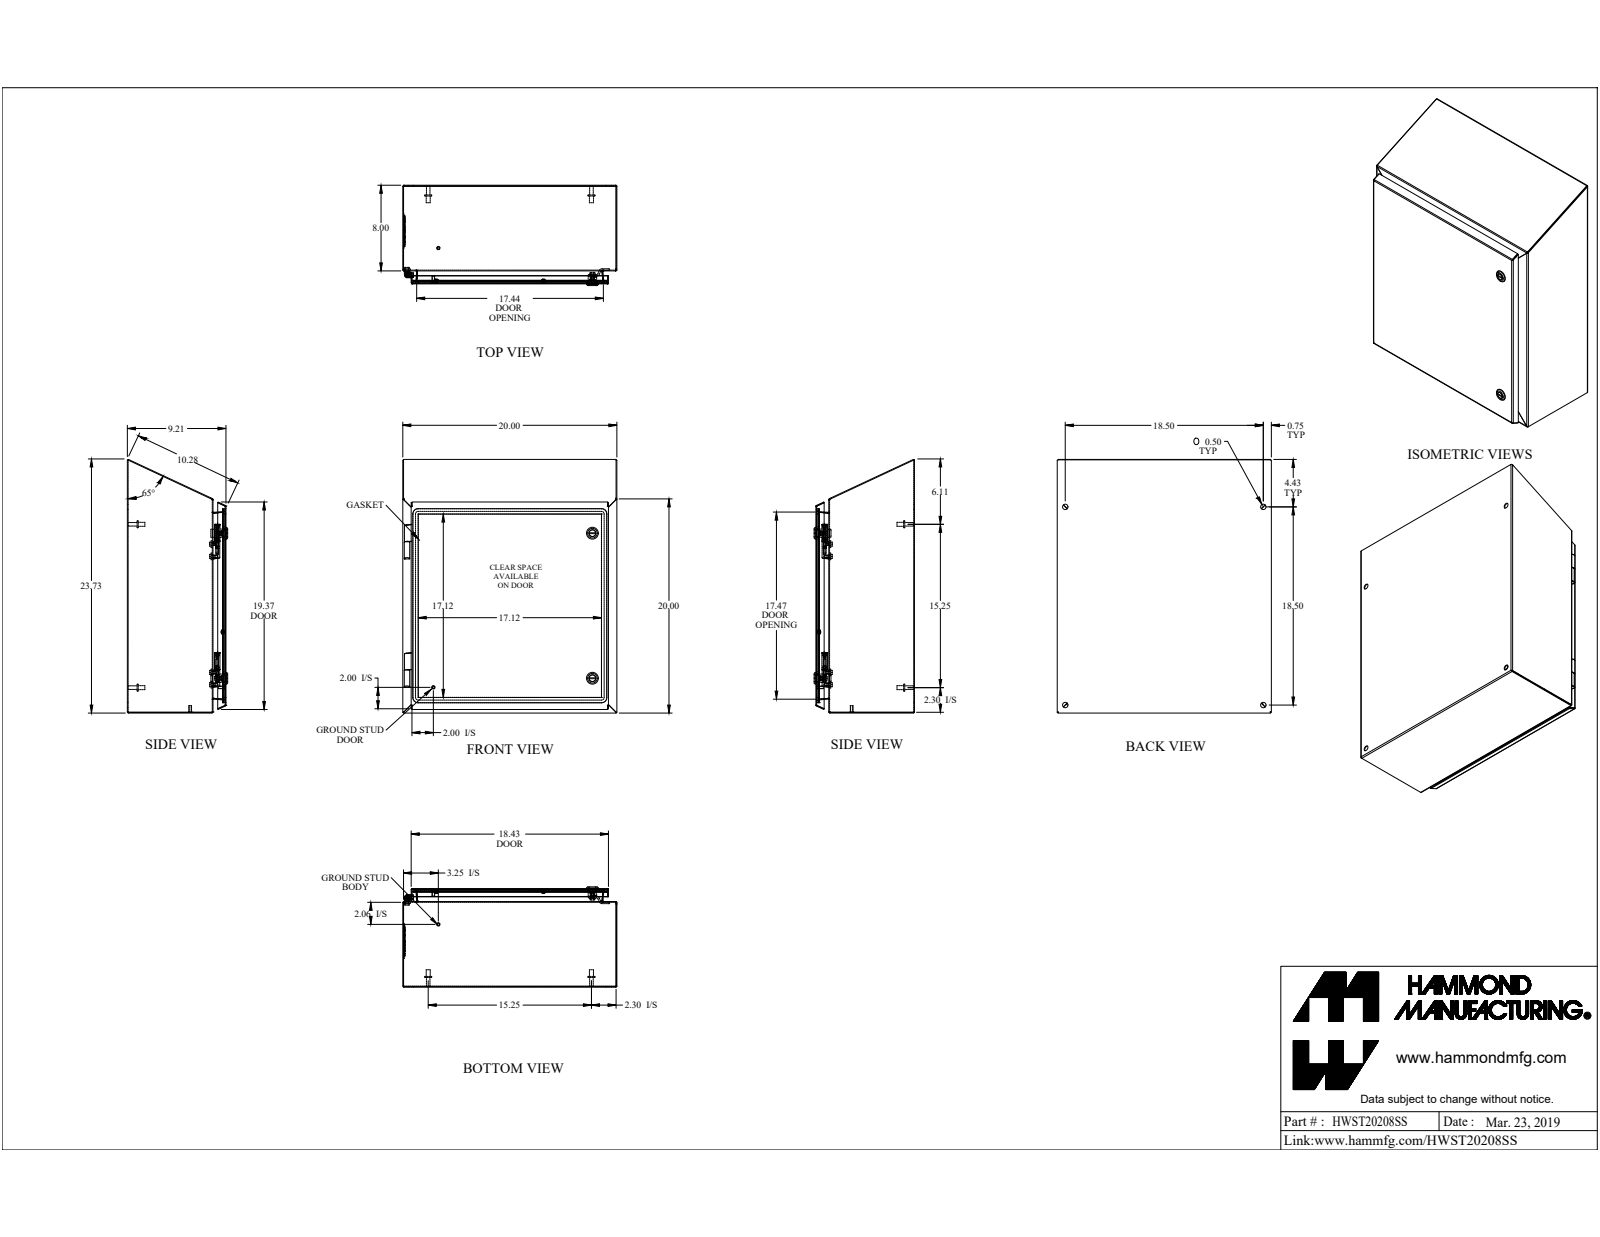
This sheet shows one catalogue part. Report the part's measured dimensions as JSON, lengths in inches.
{"part_name": "HWST20208S16", "step_written_by": "SolidWorks 2019 (AUTOMOTIVE_DESIGN)", "units": "inches", "bodies": {"solids": 43, "faces": 1037, "planar": 631, "cylindrical": 292, "other": 114}, "overall_size": [23.684, 20, 9.37], "volume_in3": 141.4, "surface_area_in2": 3810, "round_holes": [[0.194, 8], [0.5, 6], [0.24, 4], [0.275, 4], [0.13, 2], [0.197, 2], [0.387, 2], [0.63, 2], [0.768, 2], [0.24, 1], [3.5, 1]], "round_bosses_or_shafts": [[0.226, 8], [0.625, 6], [0.65, 4], [0.375, 4], [0.332, 4], [0.25, 4], [0.236, 3], [1.1, 2]], "partial_cylinders_radius": [[0.25, 24], [0.039, 16], [0.108, 16], [0.012, 12], [0.036, 12], [0.125, 12], [0.108, 9], [0.036, 7]], "face_to_face_distances": [0.072, 9.066, 9.138, 0.072, 19.928, 9.138, 9.21, 7.928, 19.856, 20], "hole_center_spacings": [1.142, 11.979, 18.5, 10.837, 11.98, 13.12, 26.163, 1.141]}
